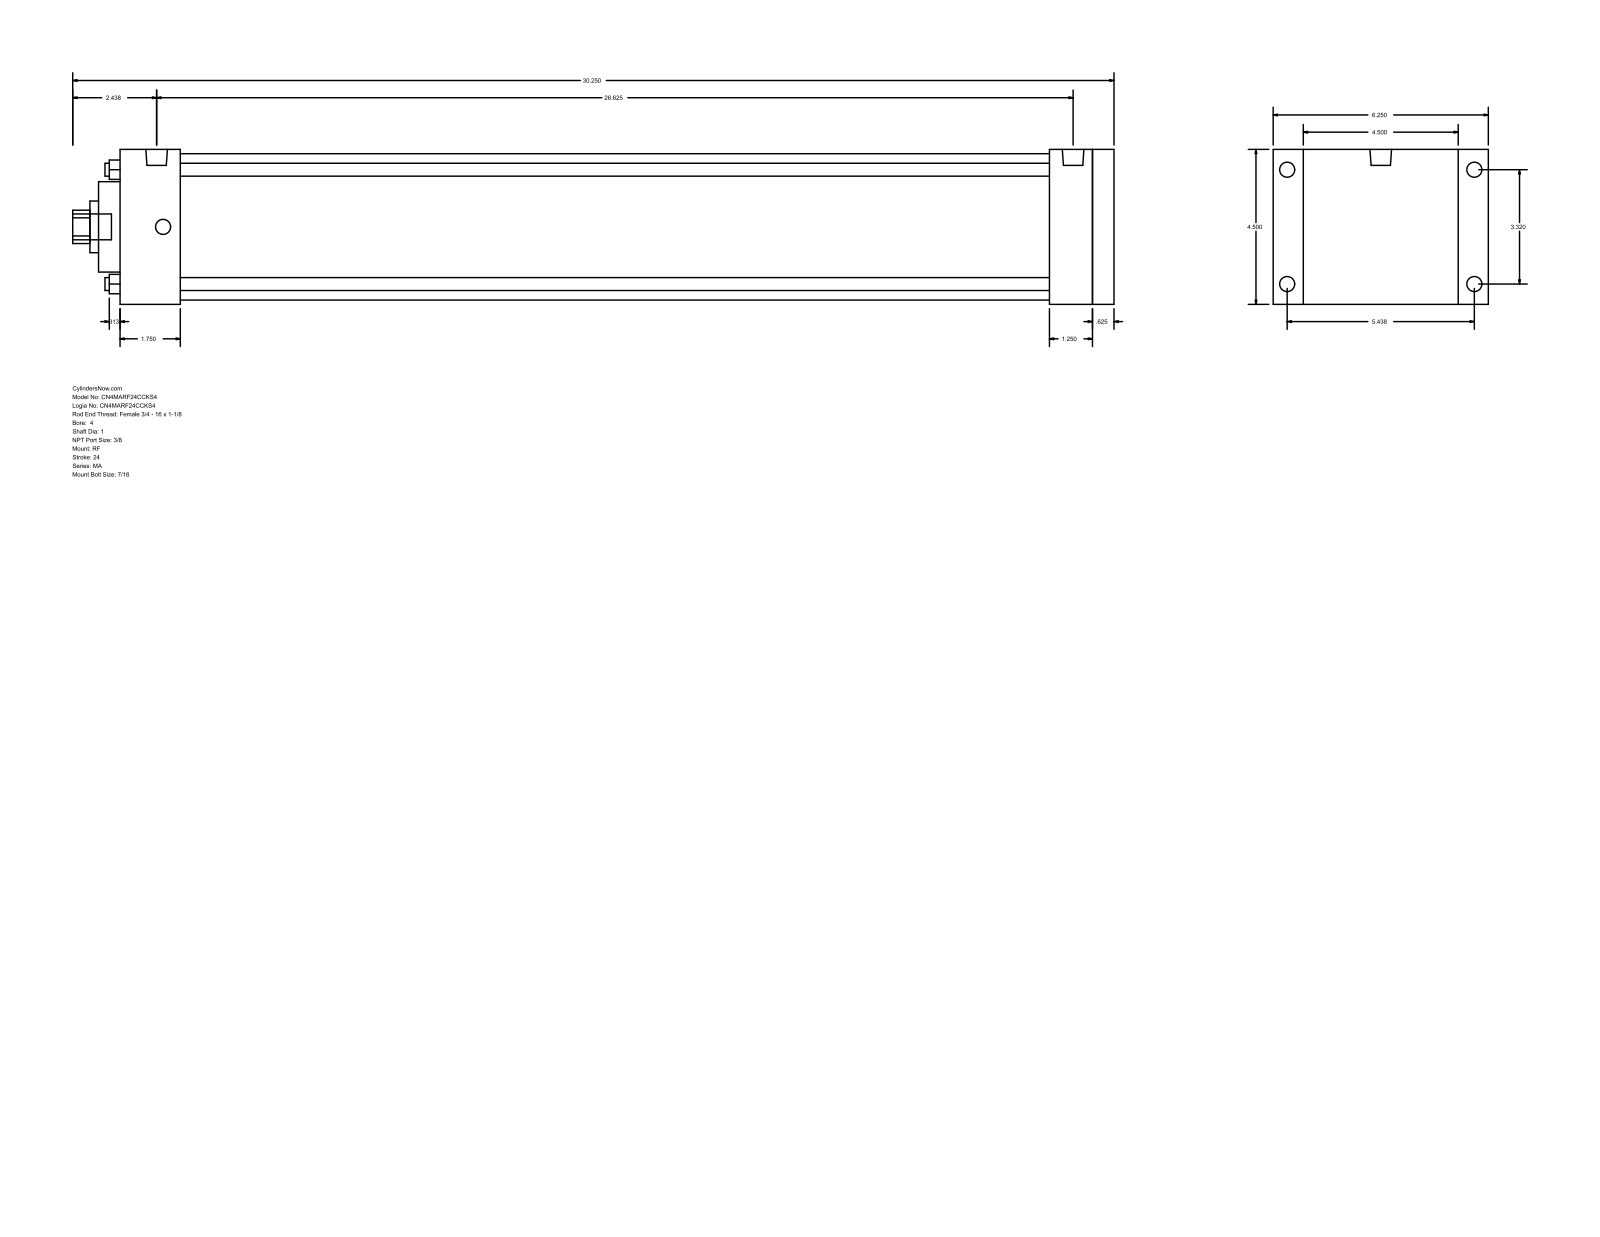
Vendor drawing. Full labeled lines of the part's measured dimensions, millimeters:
Part name (STEP PRODUCT): MA_RF__0400_1
STEP written by: GSSL Pune (CONFIG_CONTROL_DESIGN)
Units: millimetres
Bodies: 0 solids, 94 faces (65 planar, 29 cylindrical, 0 other)
Overall size (bounding box): 768.35 × 158.75 × 114.3
Round holes (diameter × count): ⌀9.53 ×4, ⌀25.4 ×1, ⌀38.1 ×1, ⌀66.67 ×1, ⌀107.95 ×1
Round bosses / shafts (diameter × count): ⌀11.11 ×8, ⌀15.93 ×2, ⌀19.05 ×1
Partial cylindrical surfaces — rounded edges, fillets, slot ends (radius × count): R12.29 ×1
Main face-to-face distances: 114.3, 733.43, 15.87, 717.56, 22.23, 136.53, 685.81, 31.75, 47.62, 44.46
Hole centre spacings: 59.62, 84.32, 119.25
